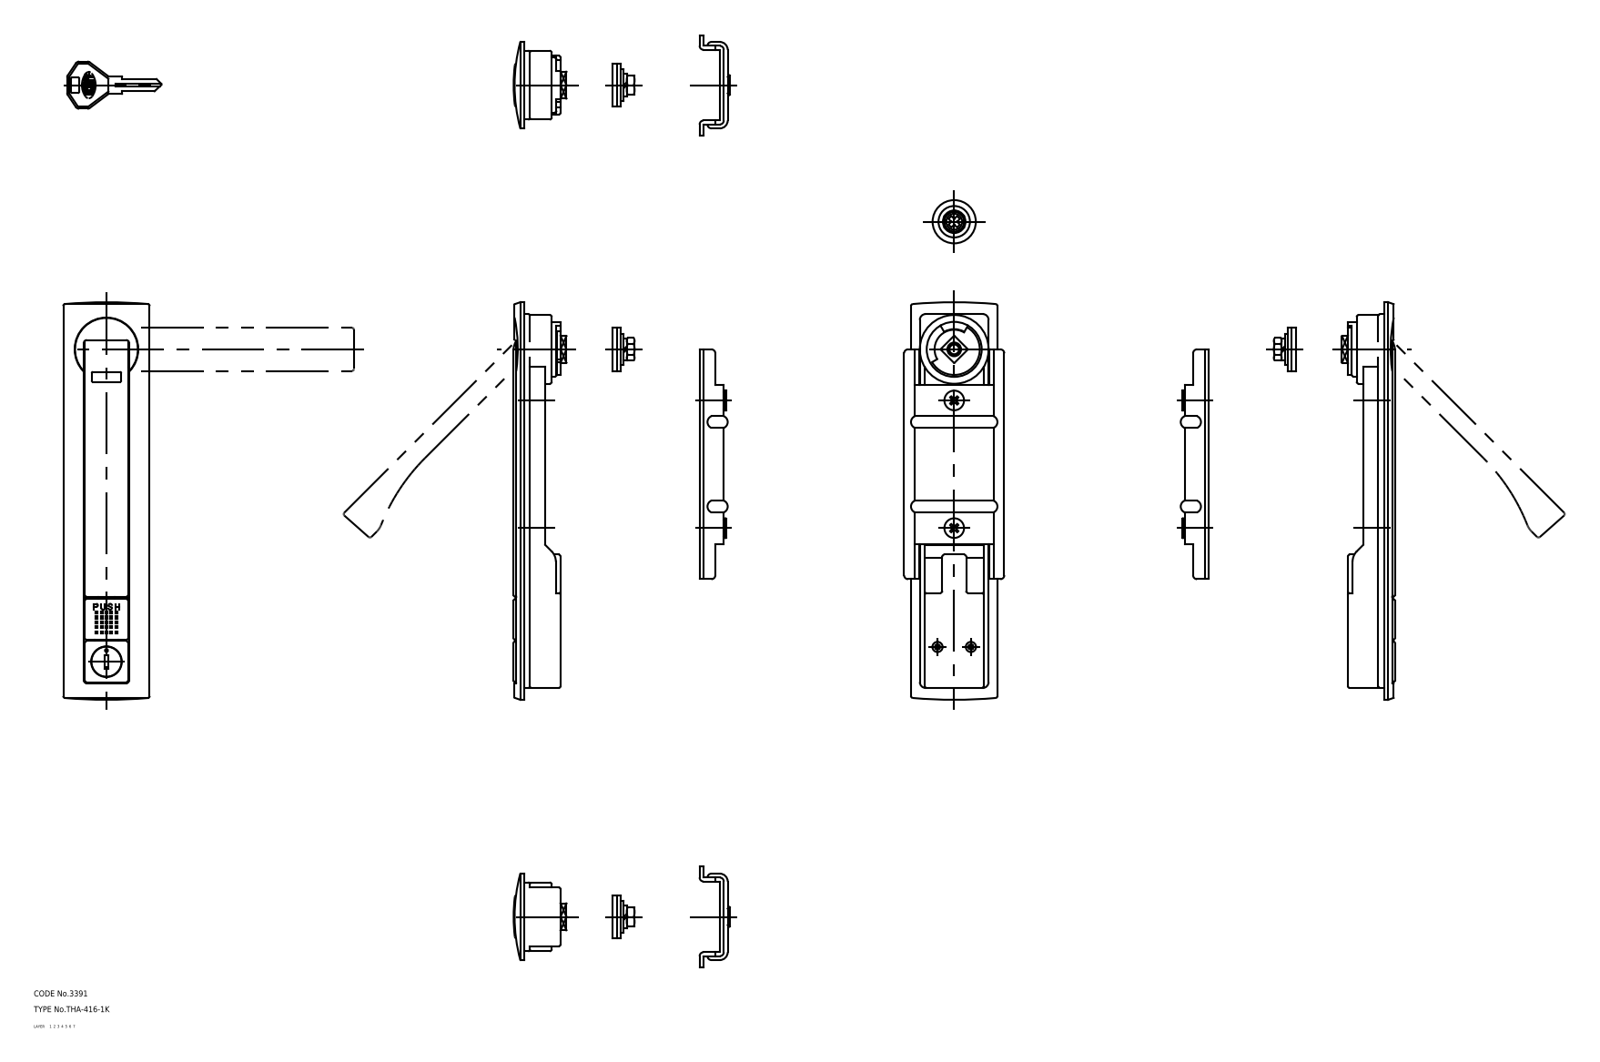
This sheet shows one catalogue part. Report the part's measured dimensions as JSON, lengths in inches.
{"part_name": "screw; washer_B; washer_A; stopper (+7 more)", "step_written_by": "CADfix (AUTOMOTIVE_DESIGN)", "units": "inches", "bodies": {"solids": 14, "faces": 501, "planar": 0, "cylindrical": 0, "other": 501}, "overall_size": [7.969, 4.633, 2.008], "volume_in3": 8.394, "surface_area_in2": 111.4}
